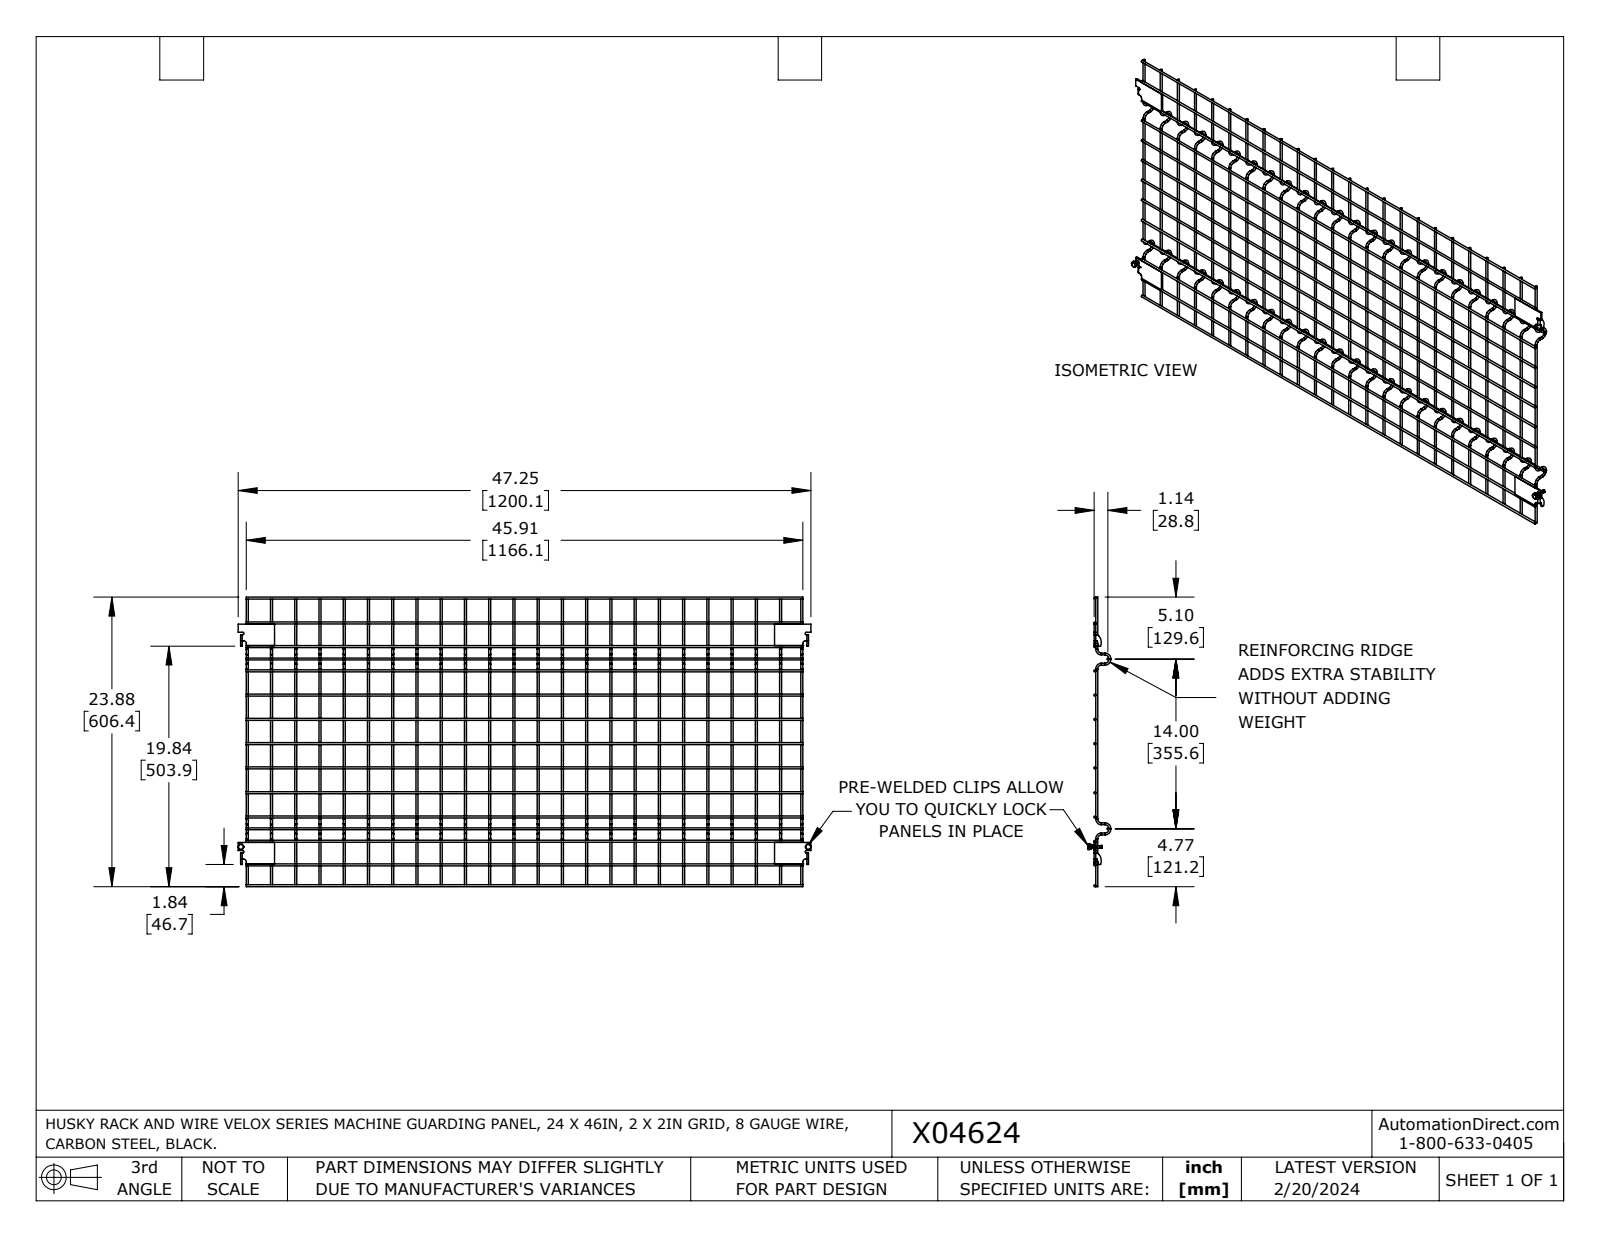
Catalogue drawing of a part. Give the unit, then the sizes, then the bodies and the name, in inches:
Units: inches
Overall size (bounding box): 47.313 × 23.875 × 1.853
Round holes (diameter × count): ⌀0.201 ×2, ⌀0.25 ×2
Round bosses / shafts (diameter × count): ⌀0.16 ×159, ⌀0.39 ×2, ⌀0.245 ×2, ⌀0.187 ×2
Partial cylindrical surfaces — rounded edges, fillets, slot ends (radius × count): R0.1 ×4, R0.218 ×4, R0.009 ×2, R0.067 ×2, R0.134 ×2, R0.25 ×2, R0.865 ×2
Main face-to-face distances: 0.134, 0.125, 2.798, 44.046, 18, 18, 0.467, 46.377, 2.331, 43.579
Hole centre spacings: 46.808
Volume: 29.58 in³ · Surface area: 721.9 in²
Bodies: 47 solids, 641 faces (158 planar, 267 cylindrical, 216 other)
Part name (STEP PRODUCT): X04624
STEP written by: SolidWorks 2023 (AUTOMOTIVE_DESIGN)
